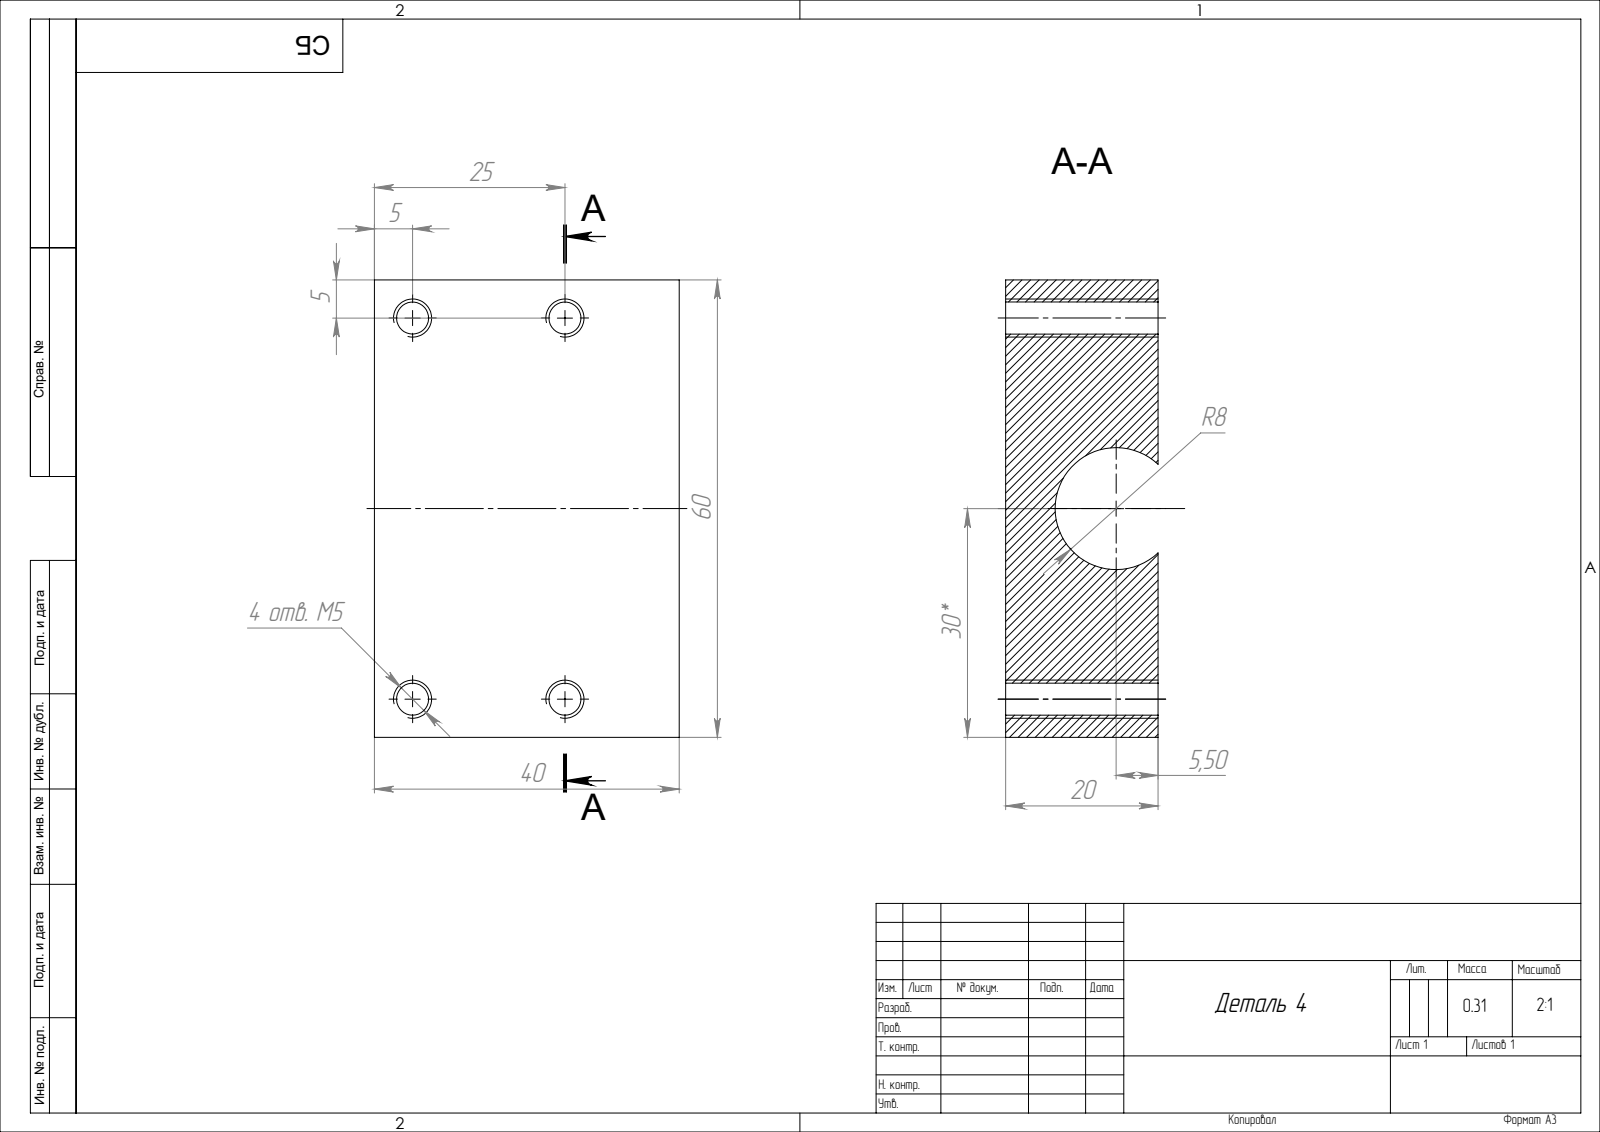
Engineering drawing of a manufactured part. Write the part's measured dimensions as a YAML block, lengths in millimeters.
part_name: "Деталь4"
step_written_by: "SolidWorks 2019 (AUTOMOTIVE_DESIGN)"
units: millimeters
bodies: {solids: 1, faces: 71, planar: 6, cylindrical: 34, other: 31}
overall_size: [65.97, 21.25, 11]
volume: 3014
surface_area: 4148
round_holes:
  - {diameter: 4.2, count: 1}
round_bosses_or_shafts:
  - {diameter: 7, count: 1}
partial_cylinders:
  - {radius: 0.2, count: 6}
  - {radius: 4.5, count: 2}
  - {radius: 6, count: 2}
  - {radius: 8, count: 2}
  - {radius: 50, count: 2}
  - {radius: 37, count: 1}
  - {radius: 47.38, count: 1}
face_to_face_distances: [1.5, 9.5, 11, 8, 2]
